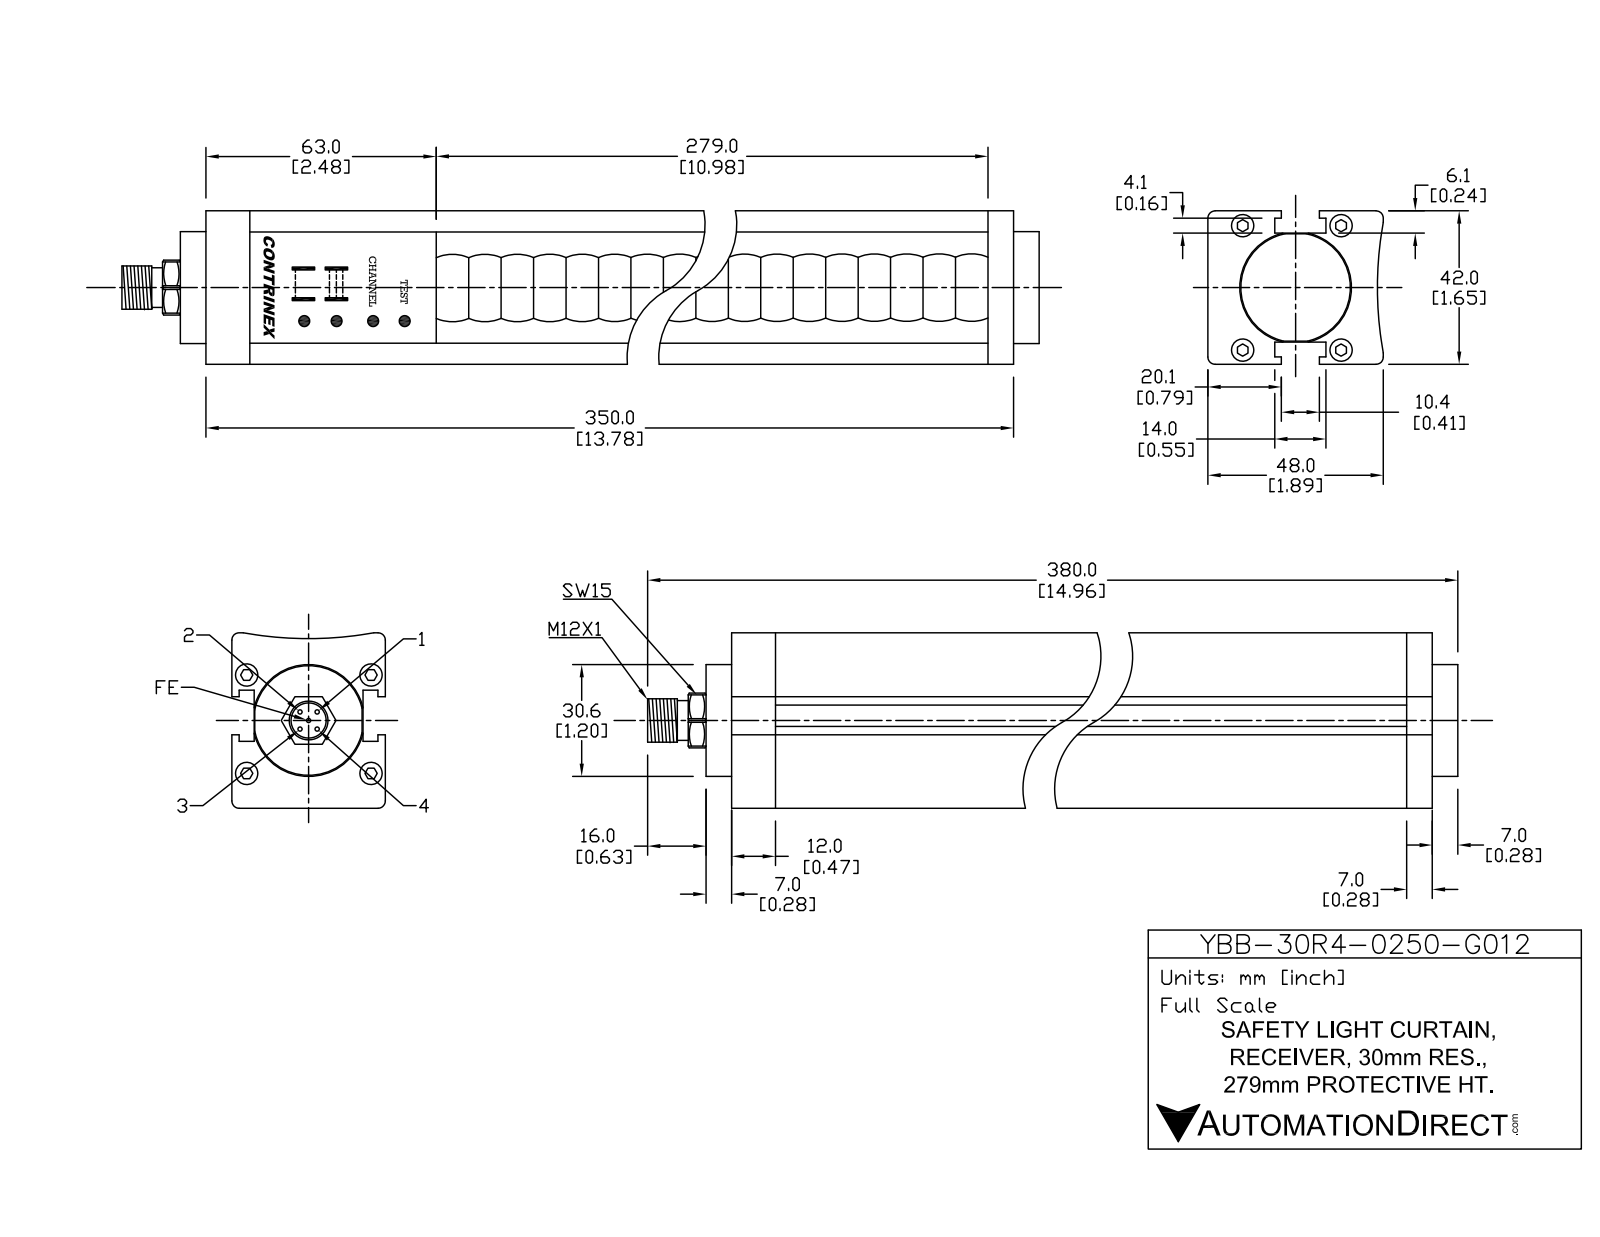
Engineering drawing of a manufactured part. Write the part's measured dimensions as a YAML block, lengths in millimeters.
part_name: "YBB-30R4-0250-G012"
step_written_by: "SolidWorks 2016 (AUTOMOTIVE_DESIGN)"
units: millimeters
bodies: {solids: 19, faces: 440, planar: 208, cylindrical: 168, other: 64}
overall_size: [380, 48, 42]
volume: 637190
surface_area: 92478
round_holes:
  - {diameter: 6, count: 4}
  - {diameter: 8.5, count: 1}
  - {diameter: 32, count: 1}
round_bosses_or_shafts:
  - {diameter: 1, count: 5}
  - {diameter: 5.5, count: 4}
  - {diameter: 30.6, count: 1}
  - {diameter: 12, count: 1}
  - {diameter: 10.5, count: 1}
partial_cylinders:
  - {radius: 1, count: 48}
  - {radius: 0.5, count: 4}
  - {radius: 0.55, count: 2}
  - {radius: 8.2, count: 1}
  - {radius: 100, count: 1}
face_to_face_distances: [6.3, 35.7, 42, 29.4, 330, 14, 17.2, 31.2, 8, 12]
hole_center_spacings: [21.04, 22.34, 26.9, 34, 43.35]
